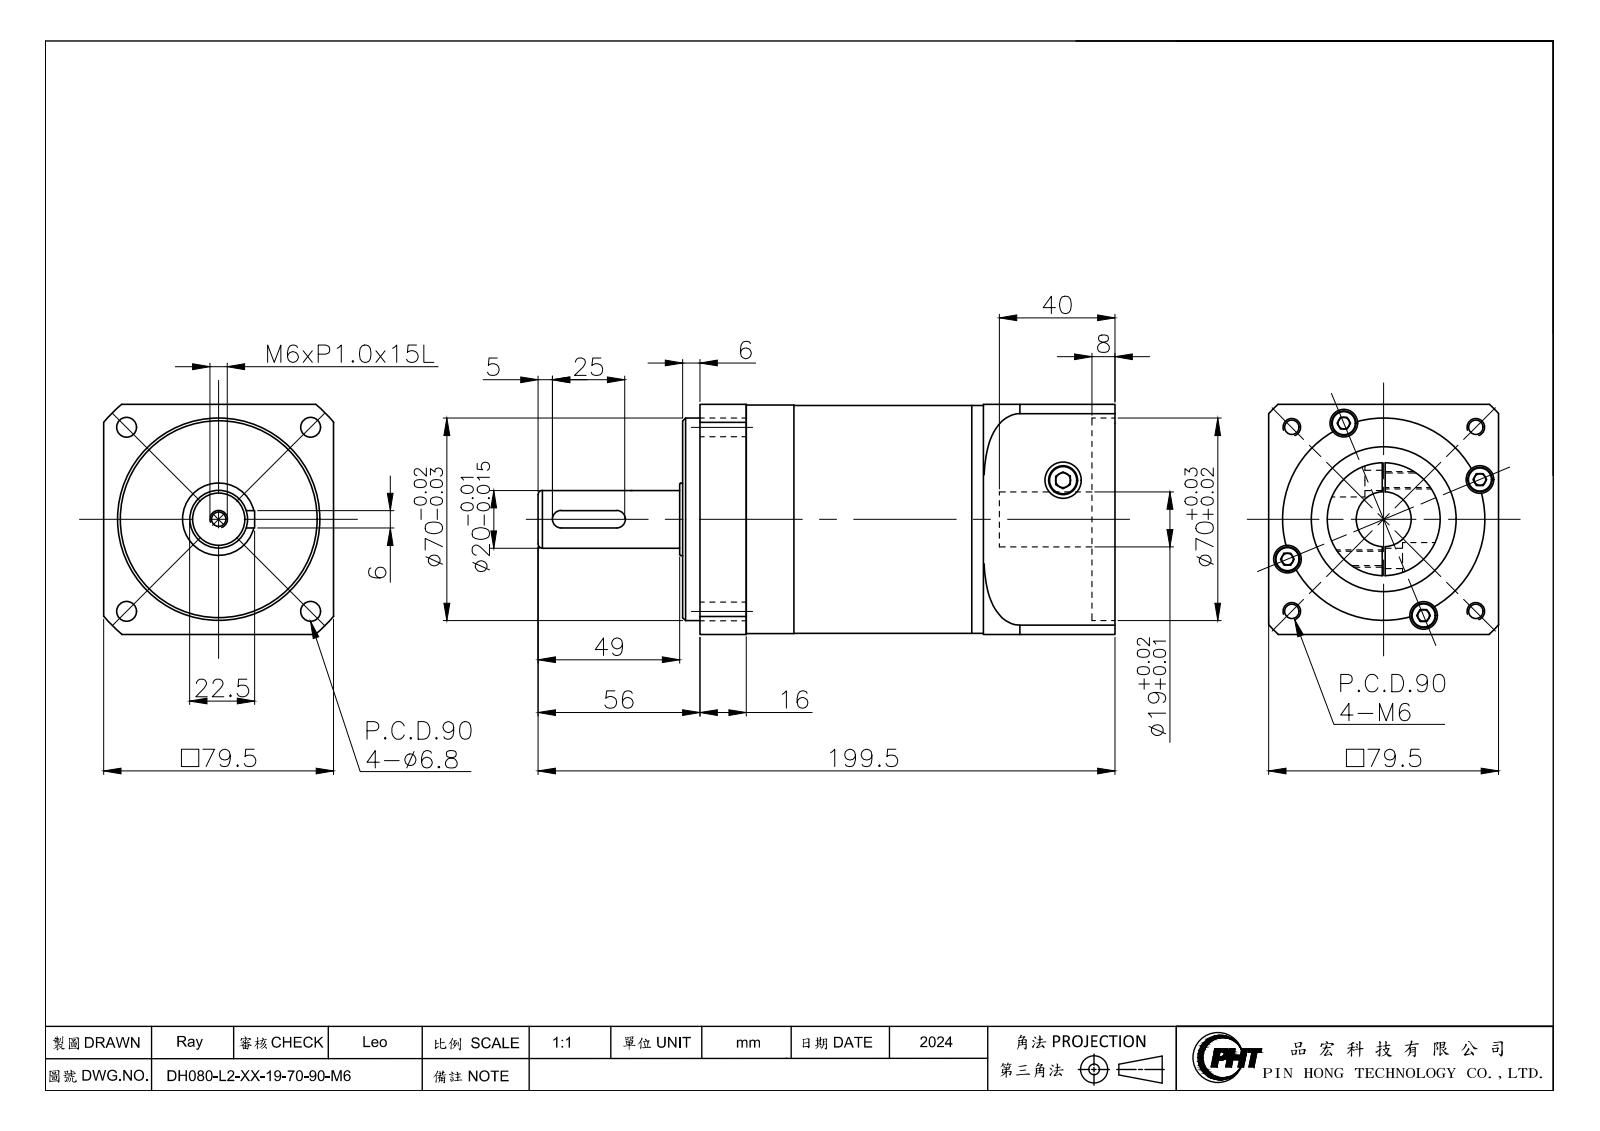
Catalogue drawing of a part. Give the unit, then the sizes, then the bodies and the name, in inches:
Units: inches
Overall size (bounding box): 7.854 × 3.13 × 3.13
Round holes (diameter × count): ⌀0.197 ×5, ⌀0.268 ×4, ⌀0.374 ×4, ⌀0.5 ×2, ⌀0.748 ×1, ⌀1.969 ×1, ⌀2.756 ×1
Round bosses / shafts (diameter × count): ⌀0.335 ×4, ⌀3.11 ×1, ⌀3.102 ×1, ⌀1.535 ×1, ⌀0.984 ×1, ⌀0.787 ×1
Partial cylindrical surfaces — rounded edges, fillets, slot ends (radius × count): R0.118 ×2, R2.126 ×1
Main face-to-face distances: 3.13, 3.937, 0.236, 3.701, 1.949, 5.65, 5.886, 5.571, 0.315, 1.634
Hole centre spacings: 0.713, 1.417, 1.772, 1.796, 2.004, 2.506, 2.659, 3.129
Volume: 45.29 in³ · Surface area: 138.9 in²
Bodies: 2 solids, 161 faces (65 planar, 74 cylindrical, 22 other)
Part name (STEP PRODUCT): DH080-L2-XX-19-70-90-M6_2024
STEP written by: SolidWorks 2016 (CONFIG_CONTROL_DESIGN)
